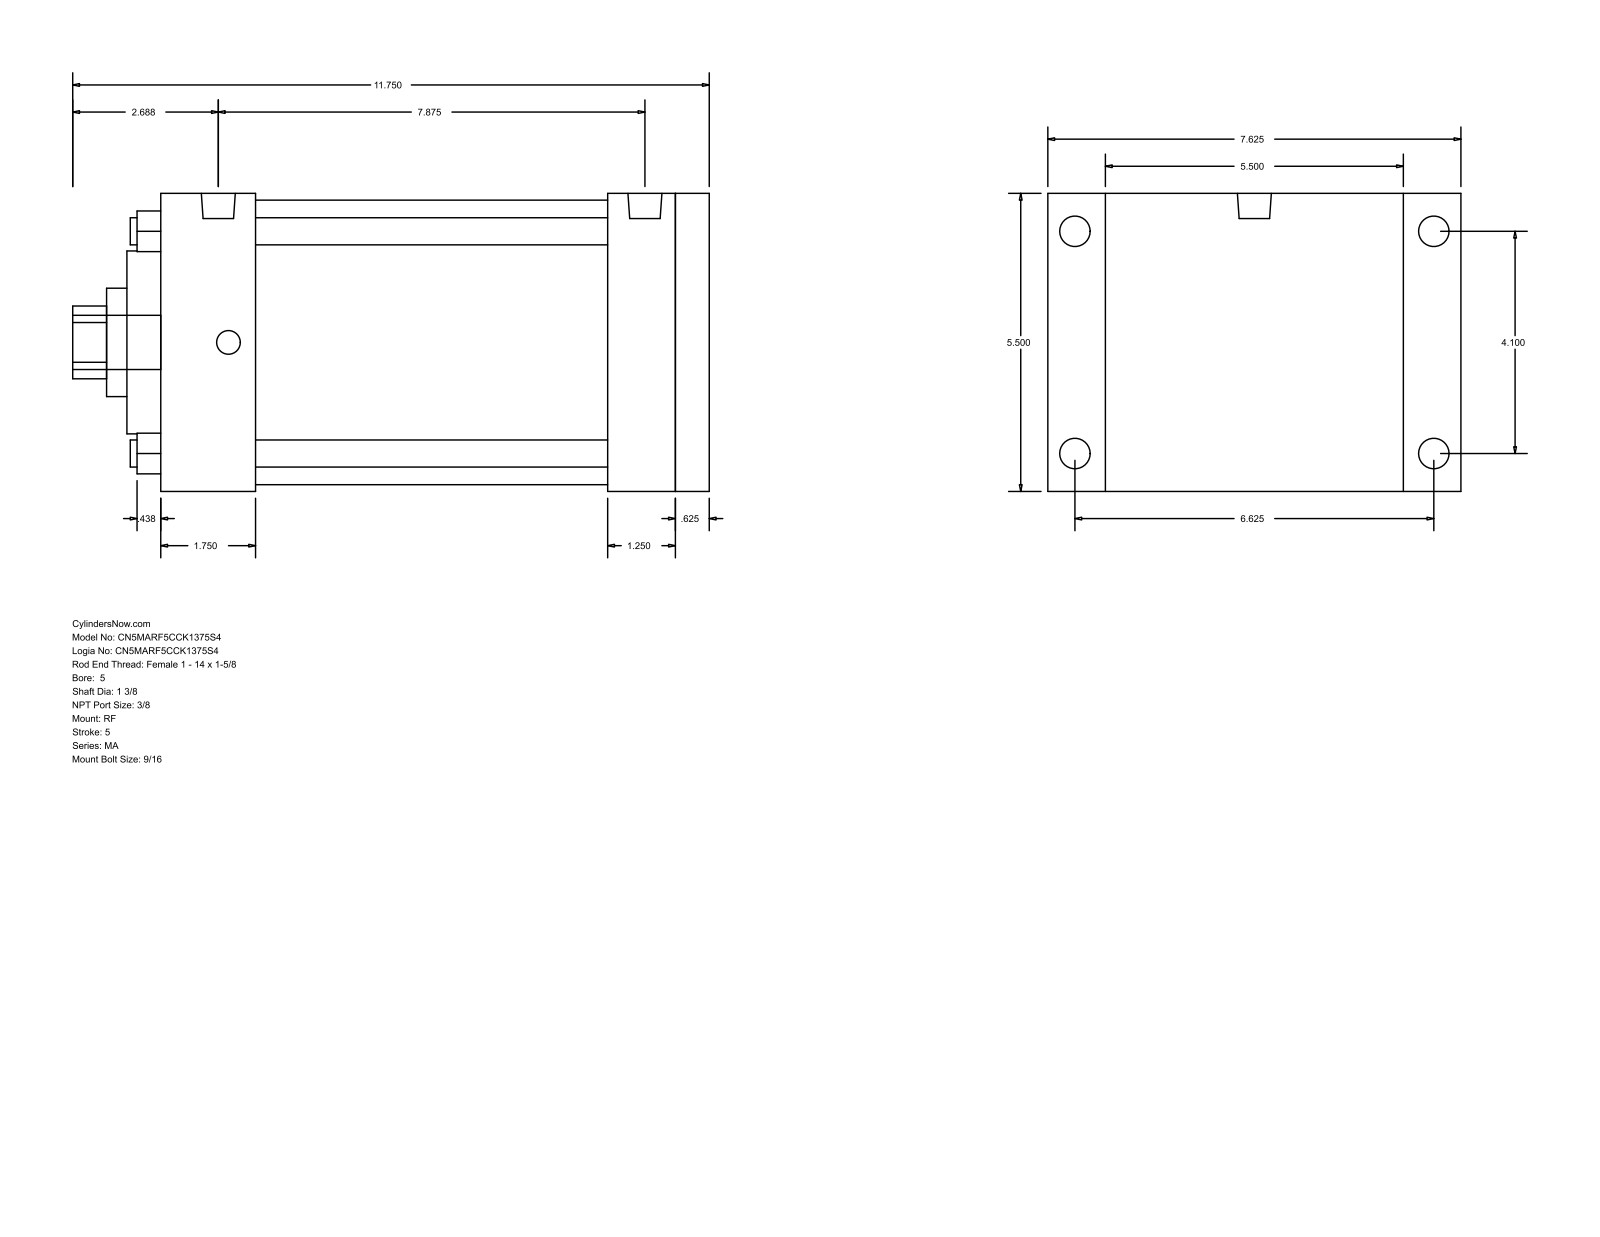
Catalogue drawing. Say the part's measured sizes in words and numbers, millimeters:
The part is named "MA_RF__0500_1.375". Its 3-D file was written by "GSSL Pune (CONFIG_CONTROL_DESIGN)". It is 0 solids with 94 faces: 65 planar, 29 cylindrical and 0 other. Overall it measures 298.45 by 193.68 by 139.7 millimeters. Round holes: 4 of diameter 12.7, 1 of diameter 34.92, 1 of diameter 50.8, 1 of diameter 85.72, 1 of diameter 133.35. Round bosses or shafts: 4 of diameter 14.29, 4 of diameter 11.11, 2 of diameter 15.93, 1 of diameter 25.4. Partial cylindrical surfaces (rounded edges, fillets, slot ends): 1 of radius 17.06. The main face-to-face distances are 139.7, 257.18, 15.88, 241.3, 44.45, 196.85, 212.73, 209.55, 165.1, 31.75. The hole center spacings are 73.64, 104.14, 147.28.
